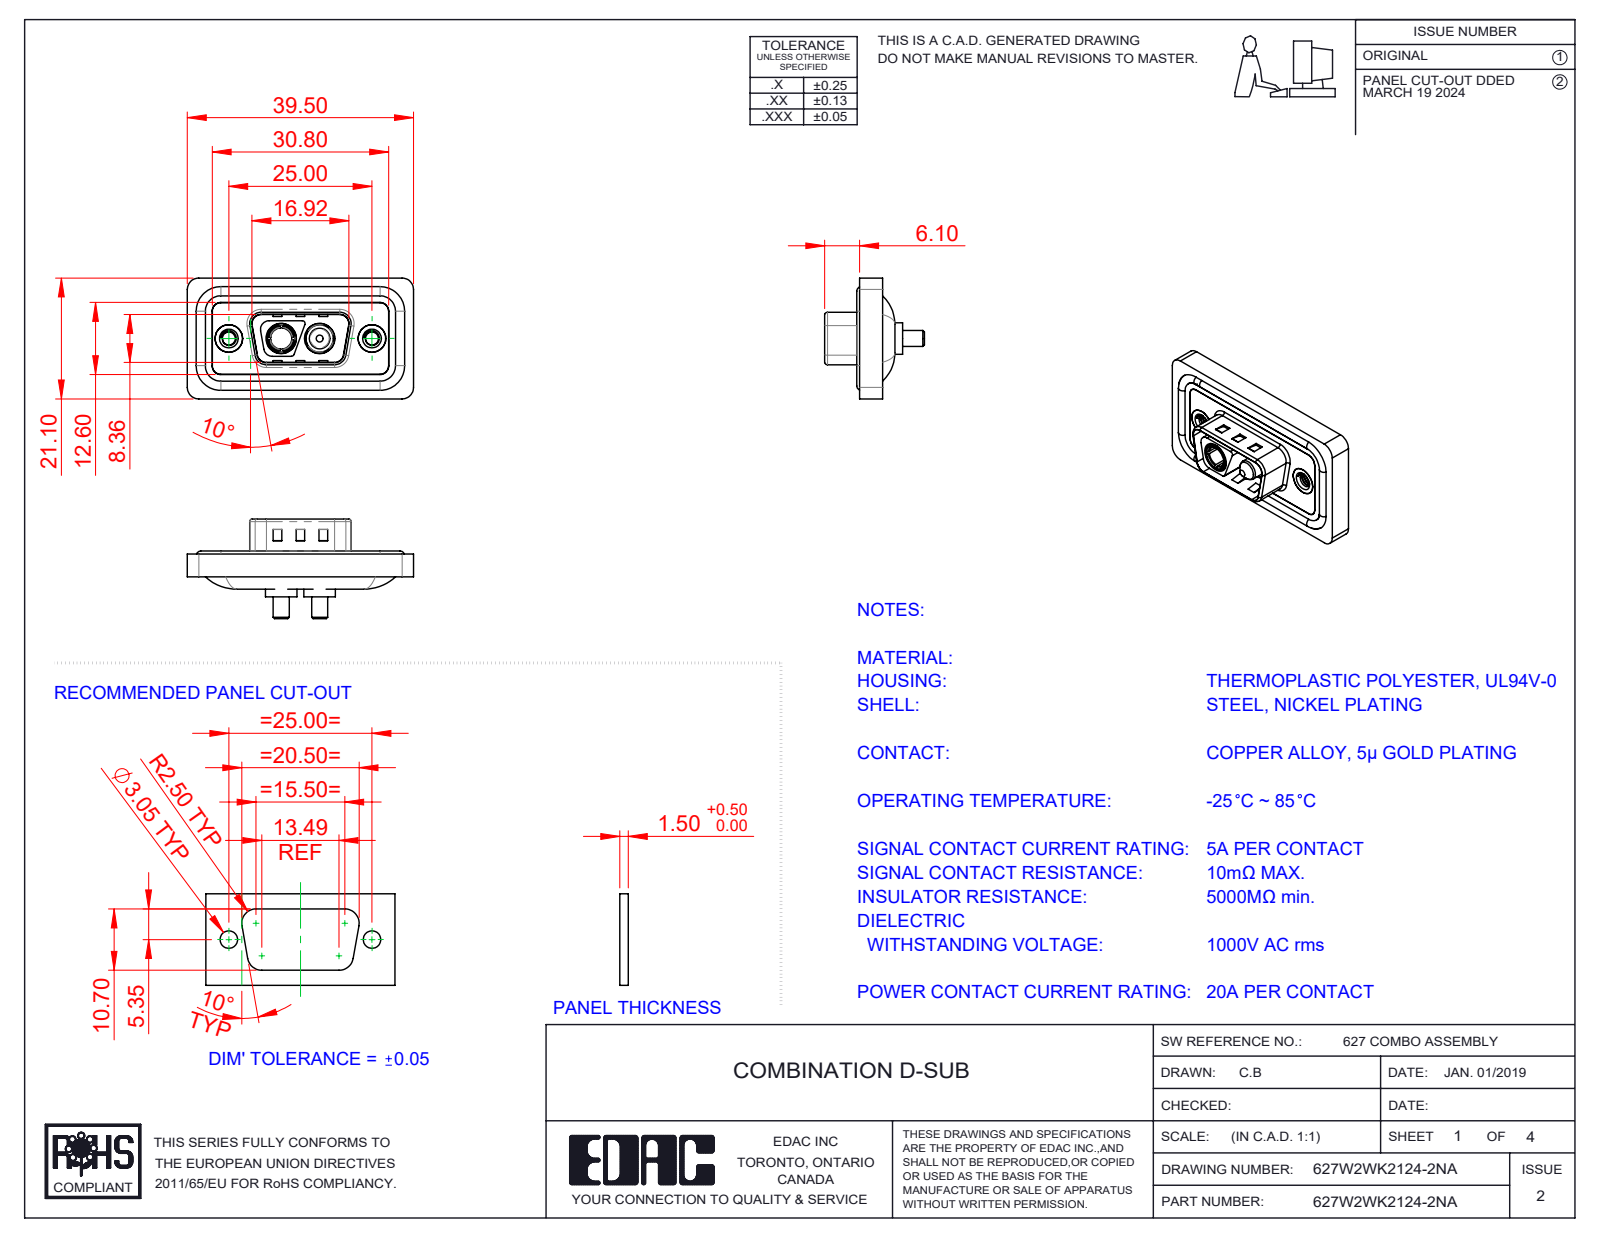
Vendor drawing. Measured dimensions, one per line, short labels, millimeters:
name: Power Pin_20A S; 627Combo Waterproof Housing_09 Contacts; 627W2WK2124-2NA; 627Combo Housing_2WK2 (+4 more)
written by: SolidWorks 2023 (CONFIG_CONTROL_DESIGN)
unit: mm
bodies: 11 solids, 532 faces (189 planar, 229 cylindrical, 114 other)
size: 39.5 × 21.1 × 17.4
volume: 4 556 mm³; area: 7 340 mm²
holes: 2× ⌀2.26, 2× ⌀4, 2× ⌀4.8, 2× ⌀4.85, 2× ⌀5, 2× ⌀5.3, 1× ⌀3.7
bosses: 4× ⌀1.6, 2× ⌀5.5, 2× ⌀5.2, 2× ⌀4.9, 2× ⌀4.75, 2× ⌀3.75, 2× ⌀2.8, 1× ⌀4.96
rounds: 24× R1.5, 18× R2, 10× R0.5, 8× R1.6, 4× R0.25, 4× R0.6, 4× R0.65, 4× R0.9
face distances: 0.4, 1.1, 2.9, 0.5, 3.1, 1.6, 1.5, 4, 2.5, 1.8
hole spacings: 9.14, 15.86, 6.72, 25
